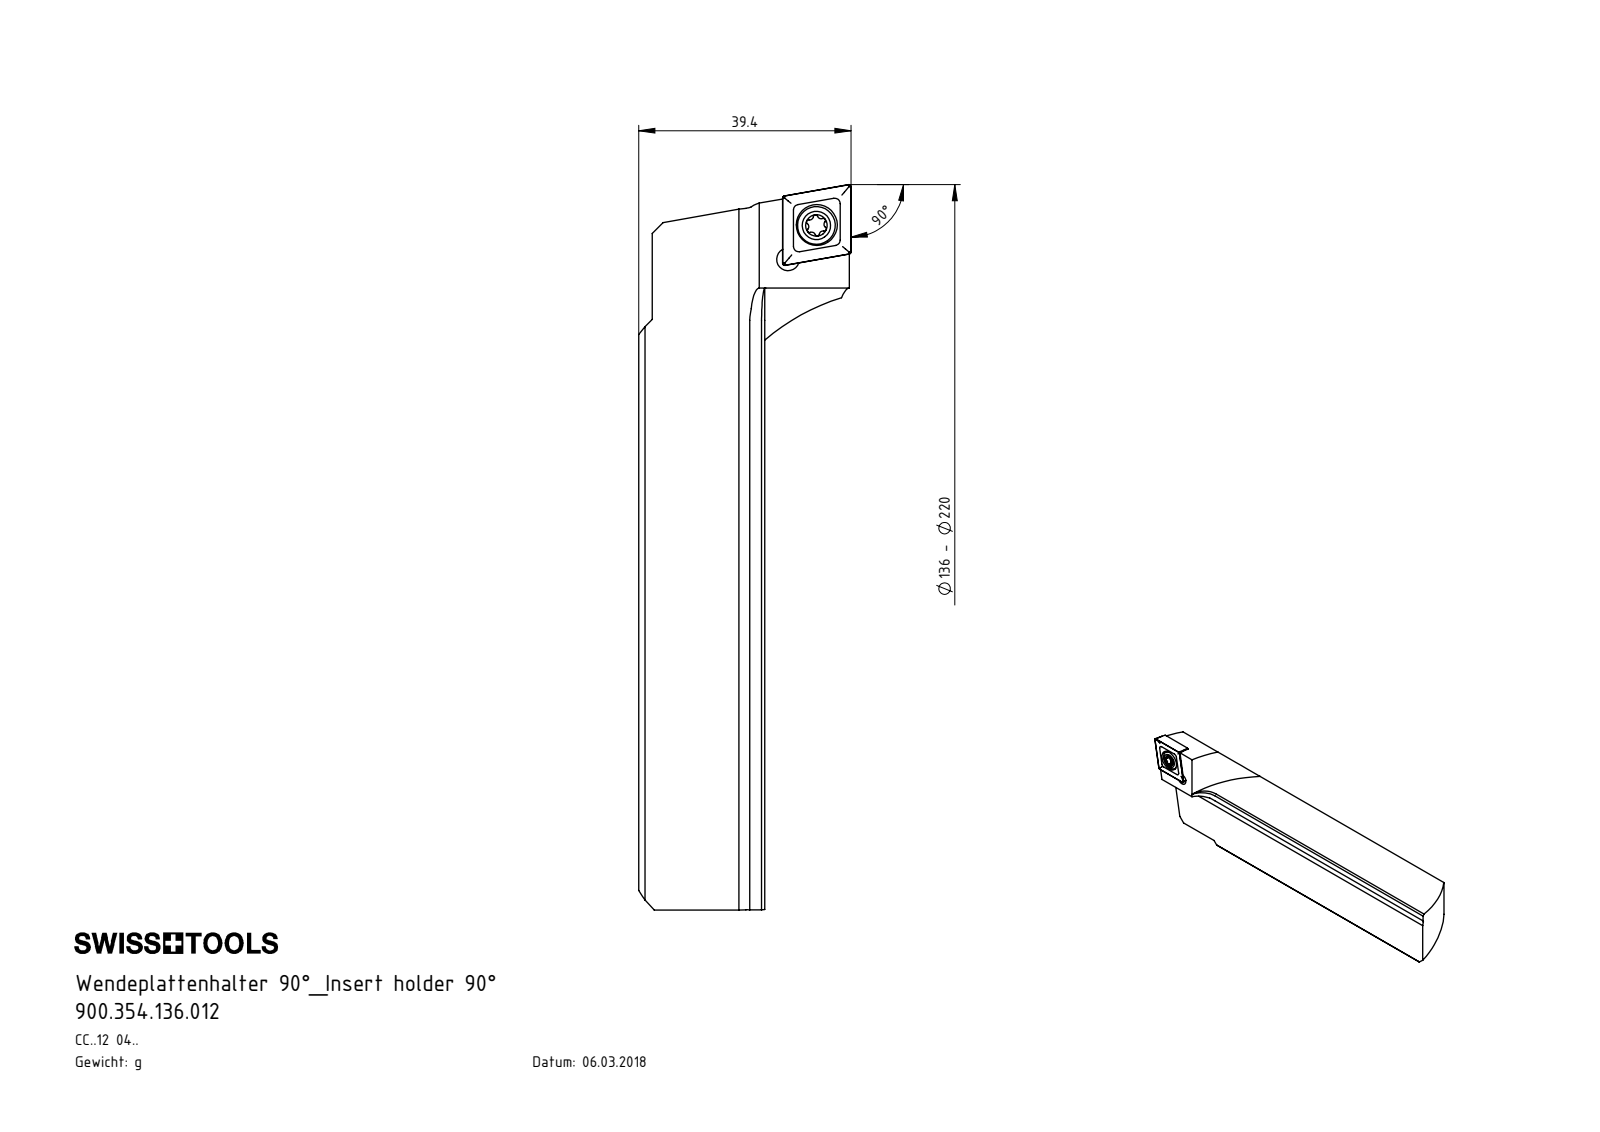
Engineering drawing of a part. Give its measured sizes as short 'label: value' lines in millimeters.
name: F00-WCC.136.001_C; 900.354.136.012; CCMT120404; WCC-ER2.001.010_A
written by: SolidWorks 2017 (CONFIG_CONTROL_DESIGN)
unit: mm
bodies: 3 solids, 556 faces (342 planar, 40 cylindrical, 174 other)
size: 134.59 × 39.4 × 27.35
volume: 55 816 mm³; area: 14 398 mm²
holes: 2× ⌀4.2, 1× ⌀5.5, 1× ⌀7.6
bosses: 1× ⌀7, 1× ⌀5
rounds: 8× R0.2, 6× R0.39, 4× R0.69, 3× R40, 2× R0.69, 1× R0.8, 1× R6
face distances: 2.38, 4.76, 21.3, 7.14, 9.52, 4.77, 7.15, 9.53, 11.91, 14.29
hole spacings: 8.21, 8.33
